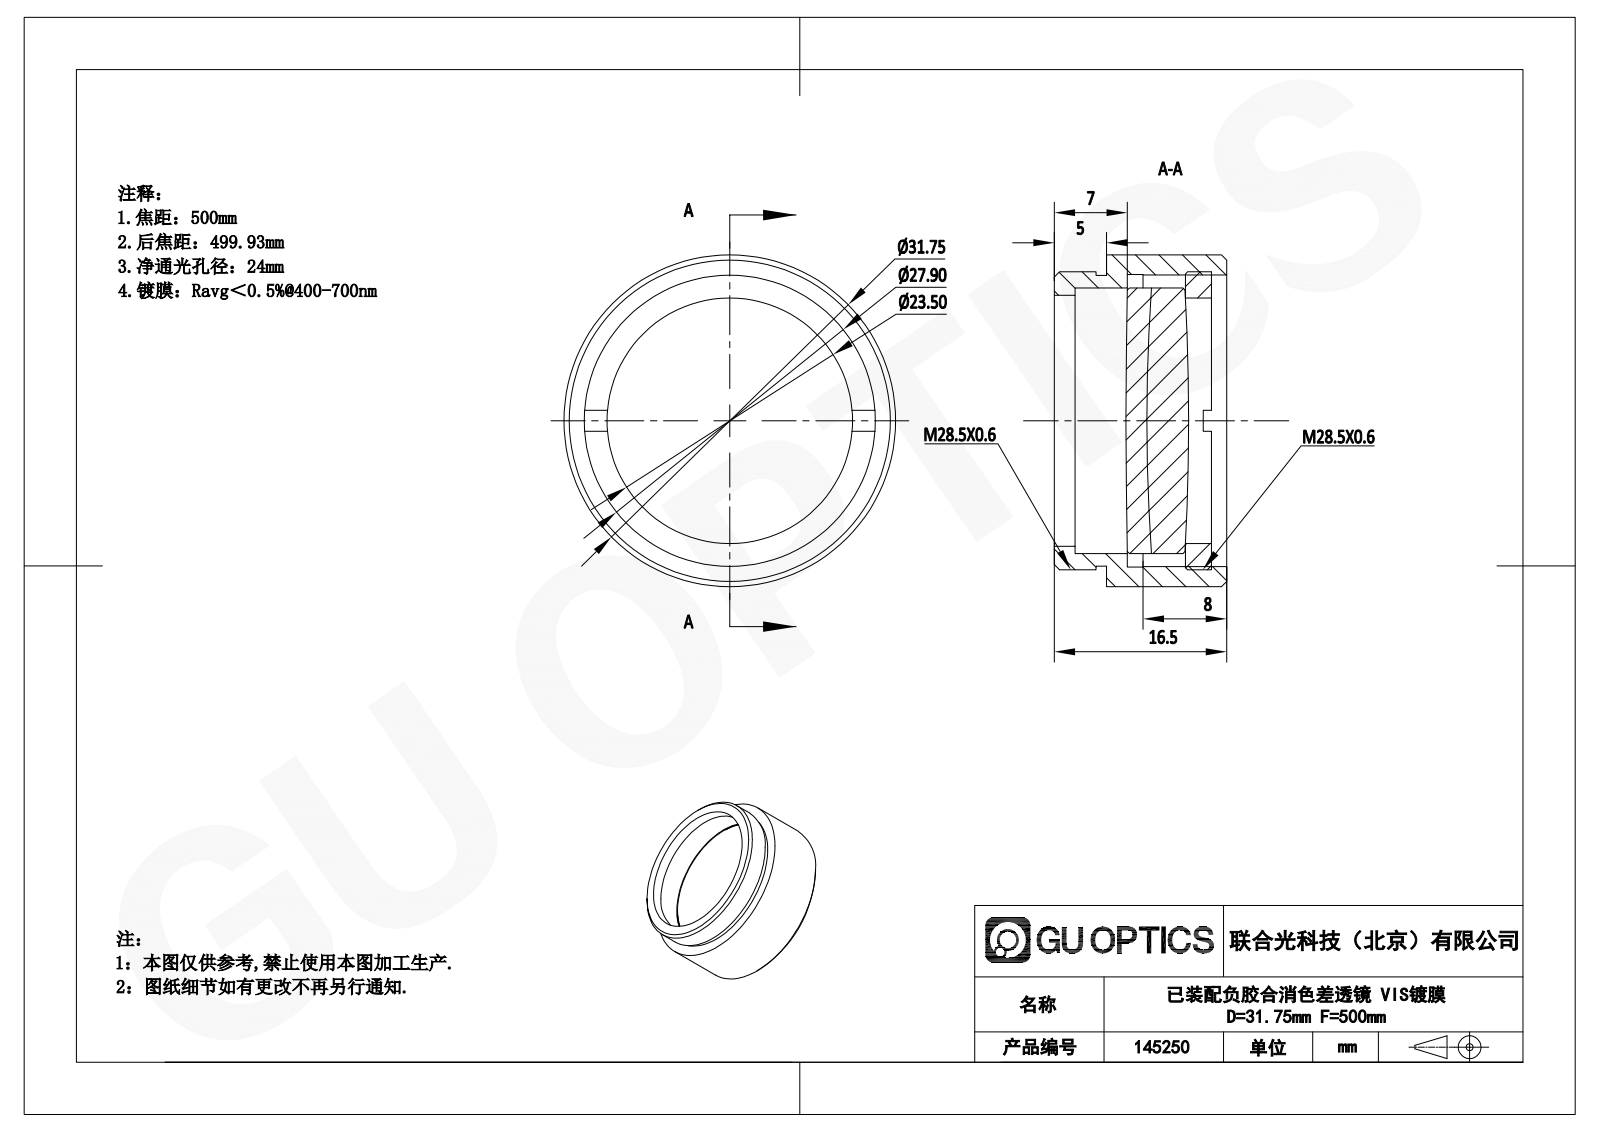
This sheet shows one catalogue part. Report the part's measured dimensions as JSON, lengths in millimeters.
{"part_name": "GL31-025B-500-VIS_Solidworks; APD-ML25-500-VIS; M28.5x0.6ѹȦ", "step_written_by": "SolidWorks 2022 (AUTOMOTIVE_DESIGN)", "units": "millimeters", "bodies": {"solids": 4, "faces": 56, "planar": 16, "cylindrical": 22, "other": 18}, "overall_size": [31.76, 31.76, 16.5], "volume_mm3": 6426, "surface_area_mm2": 6935, "round_holes": [[23.5, 1], [24, 1], [27.9, 1], [28, 1]], "round_bosses_or_shafts": [[31.76, 1], [28.5, 1], [27.8, 1], [25.4, 1]], "face_to_face_distances": [2, 5, 2.5, 7.64, 10.14, 12.64, 15.14, 16.5, 11.5, 3.86]}
